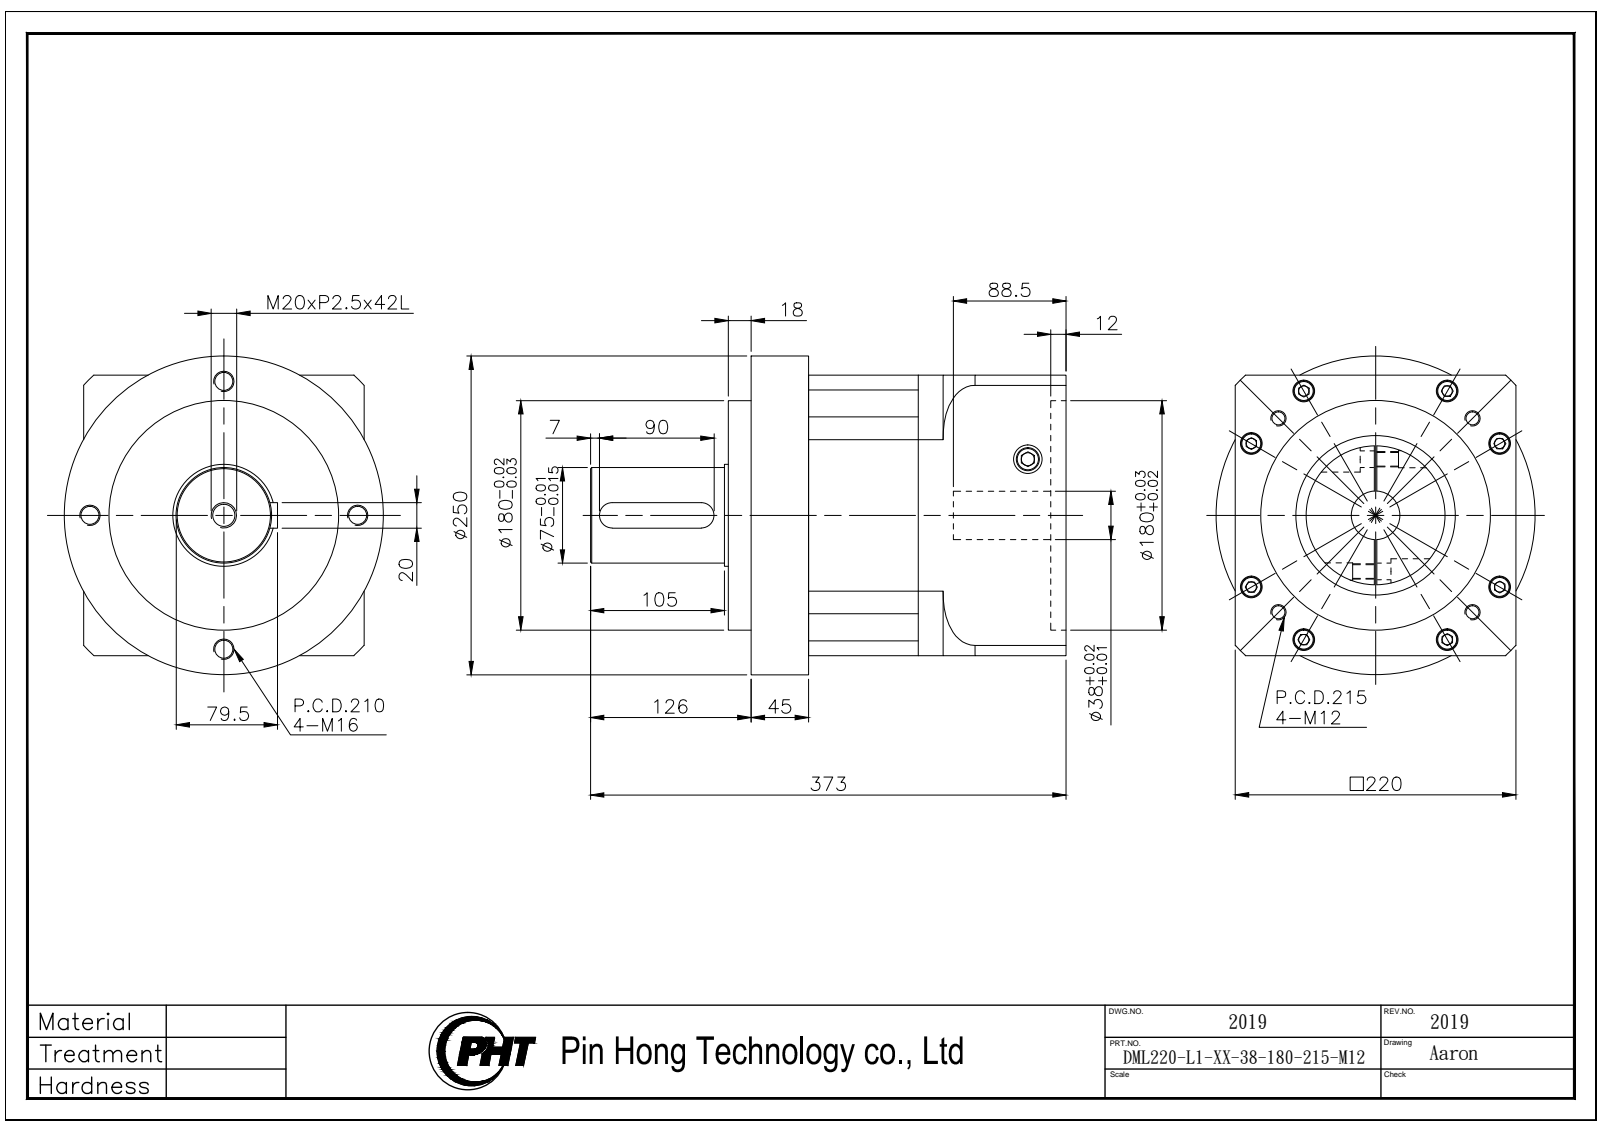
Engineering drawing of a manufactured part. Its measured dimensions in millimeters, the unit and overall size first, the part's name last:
Units: millimetres
Overall size (bounding box): 373 × 250 × 250
Round holes (diameter × count): ⌀11 ×8, ⌀17 ×8, ⌀10.2 ×4, ⌀14 ×4, ⌀22.5 ×2, ⌀17.5 ×1, ⌀38 ×1, ⌀125 ×1, ⌀180 ×1
Round bosses / shafts (diameter × count): ⌀16 ×8, ⌀250 ×1, ⌀109 ×1, ⌀80 ×1, ⌀75 ×1
Partial cylindrical surfaces — rounded edges, fillets, slot ends (radius × count): R15 ×4, R10 ×2, R150 ×1
Main face-to-face distances: 86, 220, 131, 45, 202, 116, 247, 265, 149, 63
Hole centre spacings: 112.5, 29.14, 56.76, 81.35, 108.95, 133.98, 159.1, 174.56
Volume: 11 490 000 mm³ · Surface area: 666 268 mm²
Bodies: 3 solids, 261 faces (108 planar, 113 cylindrical, 40 other)
Part name (STEP PRODUCT): DML220-L1-XX-38-180-215-M12_2019
STEP written by: SolidWorks 2016 (AUTOMOTIVE_DESIGN)
